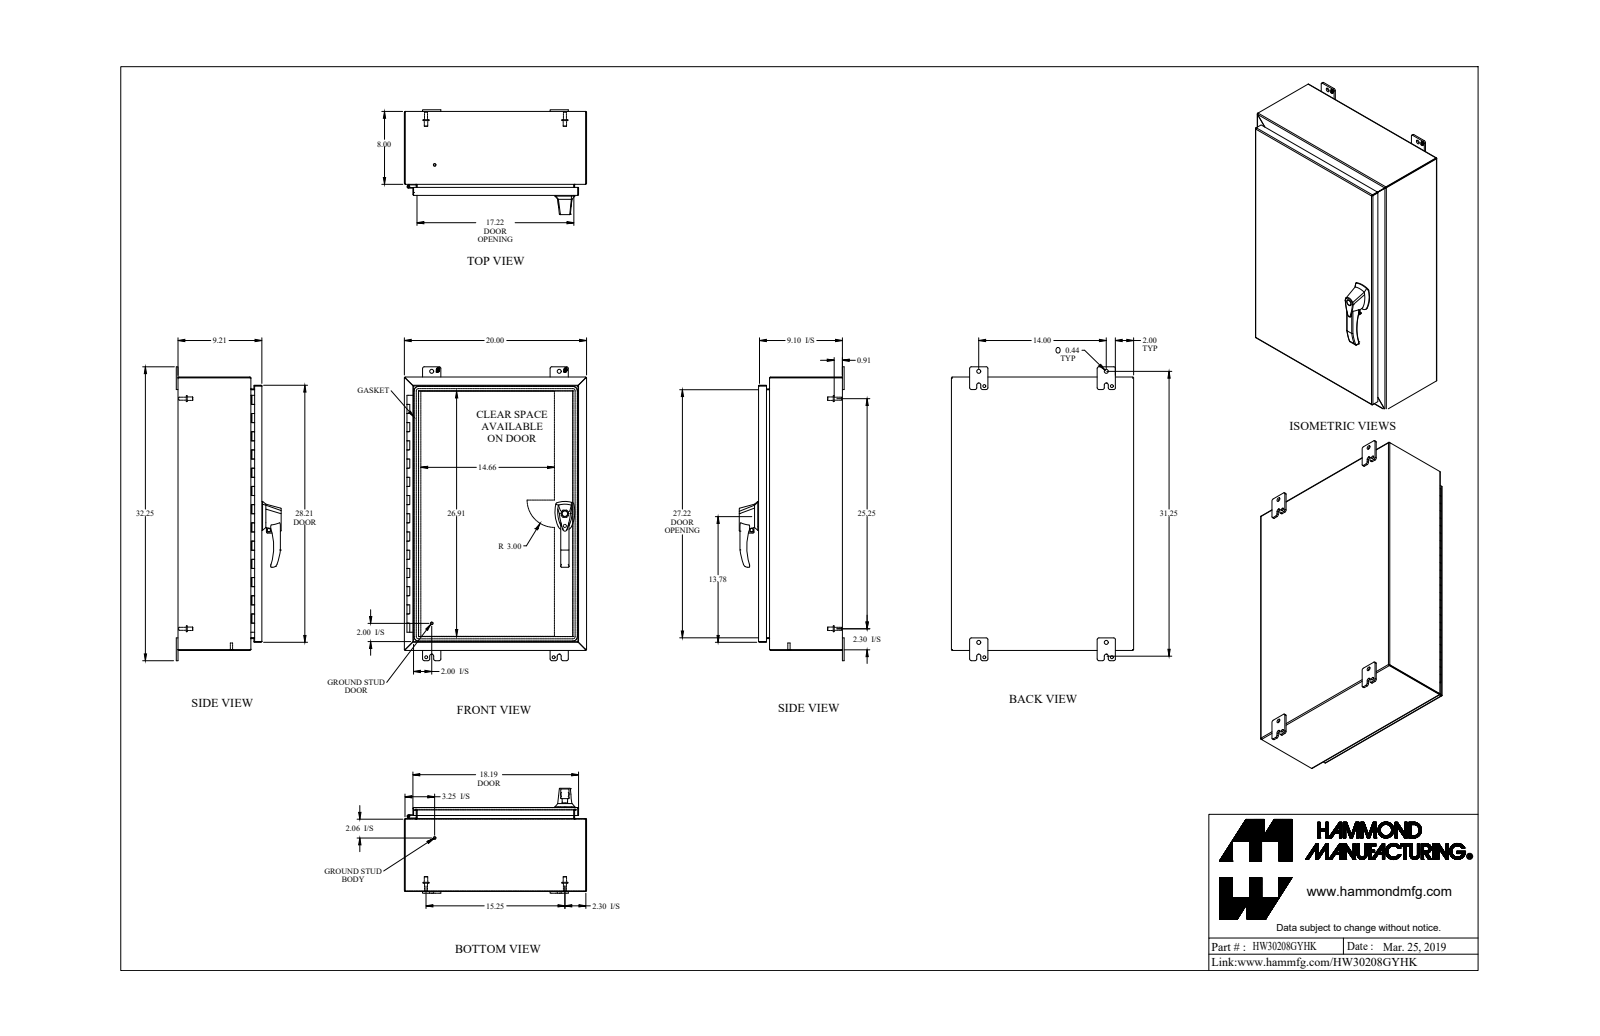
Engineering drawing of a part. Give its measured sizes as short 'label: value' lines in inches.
name: HW30208GYHK
written by: SolidWorks 2018 (AUTOMOTIVE_DESIGN)
unit: in
bodies: 41 solids, 1459 faces (715 planar, 587 cylindrical, 157 other)
size: 32.25 × 20 × 11.512
volume: 197.6 in³; area: 5 040 in²
holes: 6× ⌀0.176, 4× ⌀0.25, 4× ⌀0.313, 3× ⌀0.196, 3× ⌀0.265, 3× ⌀0.413, 2× ⌀0.256, 2× ⌀0.394, 2× ⌀0.437, 1× ⌀0.187, 1× ⌀0.233, 1× ⌀0.334
bosses: 9× ⌀0.375, 6× ⌀0.25, 6× ⌀0.156, 4× ⌀0.65, 4× ⌀0.33, 3× ⌀1, 2× ⌀0.63, 2× ⌀0.51
rounds: 27× R0.25, 24× R0.188, 20× R0.036, 20× R0.108, 12× R0.06, 9× R0.125, 8× R0.045, 8× R0.218
face distances: 0.072, 0.072, 9.138, 9.066, 9.21, 9.138, 19.928, 29.928, 7.928, 19.856
hole spacings: 11.118, 11.119, 22.237, 1.111, 7.877, 11.119, 14, 31.381
